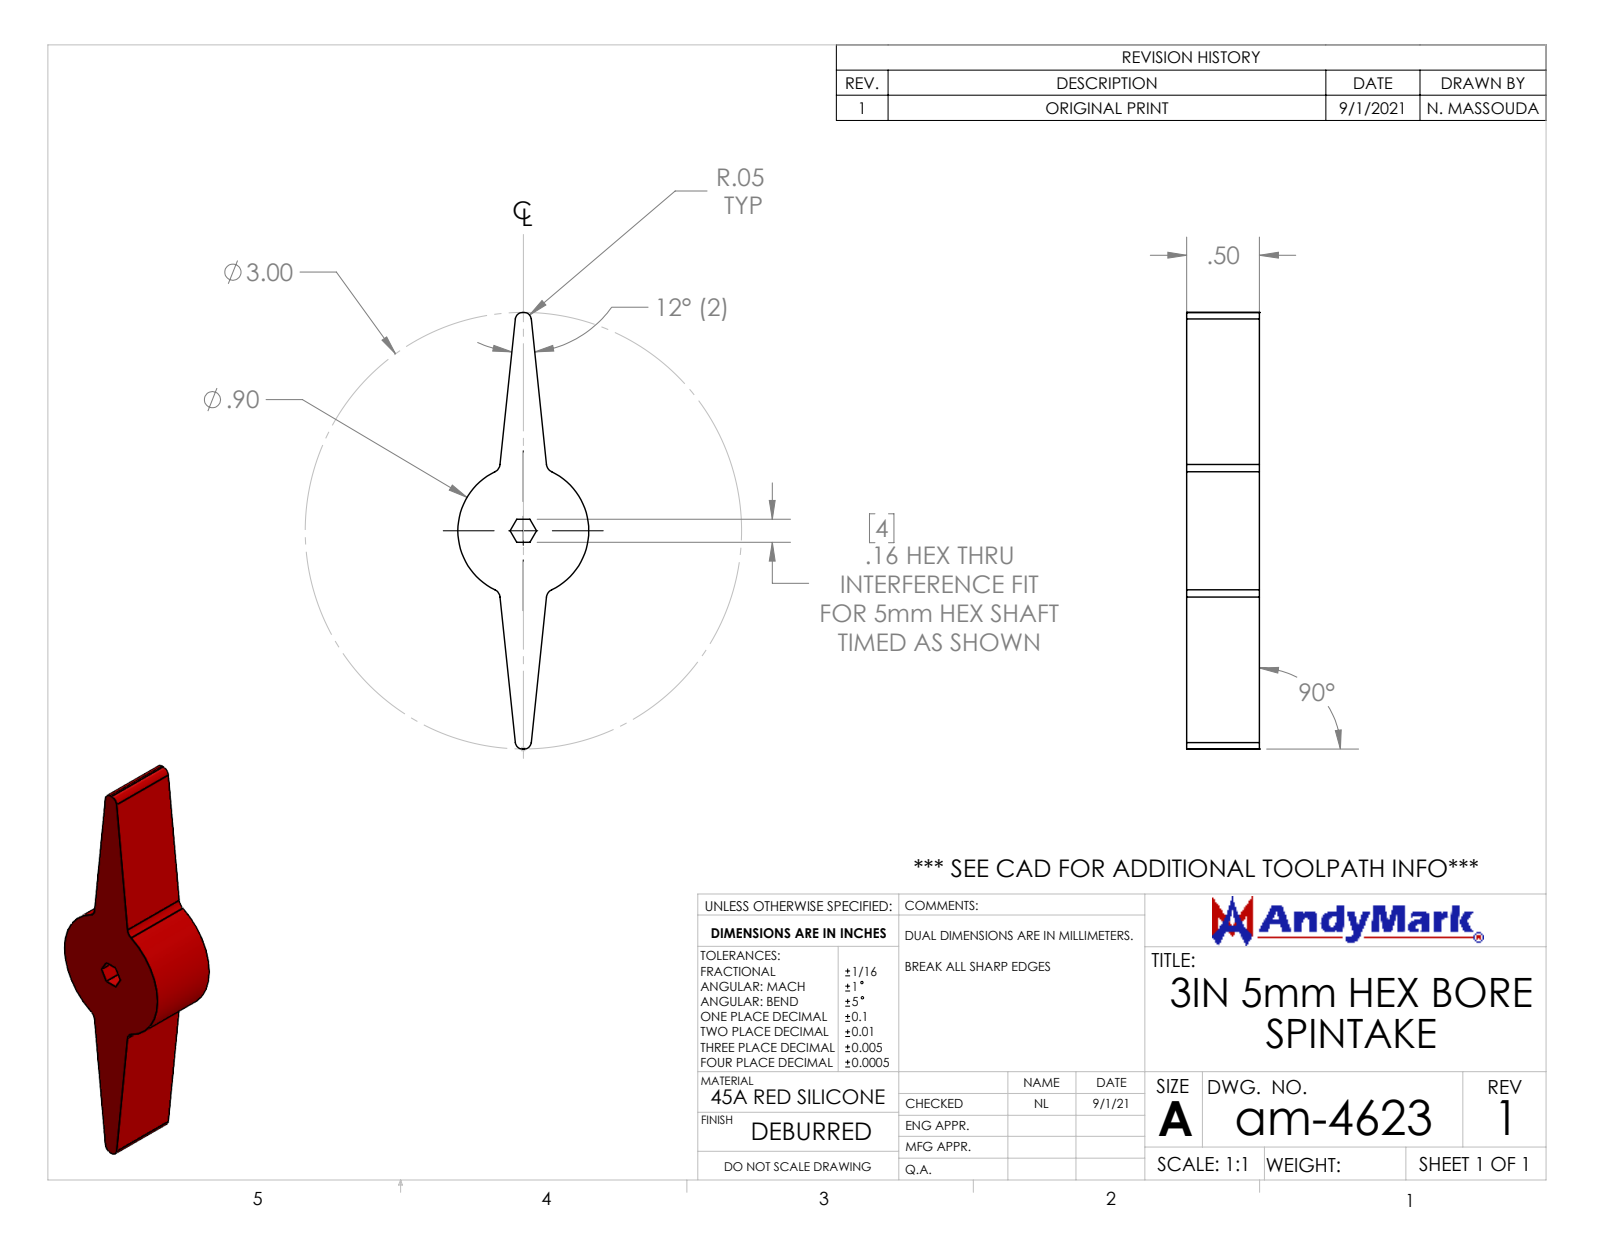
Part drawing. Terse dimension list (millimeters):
name: am-4623 3in 5mm Hex Bore SpinTake
written by: SolidWorks 2021 (AUTOMOTIVE_DESIGN)
unit: mm
bodies: 1 solid, 25 faces (12 planar, 13 cylindrical, 0 other)
size: 76.2 × 22.9 × 12.7
volume: 8 700 mm³; area: 3 678 mm²
rounds: 4× R1.3, 3× R1.6, 1× R1.6, 1× R11.4, 1× R38.1
face distances: 12.7, 10.5, 4
